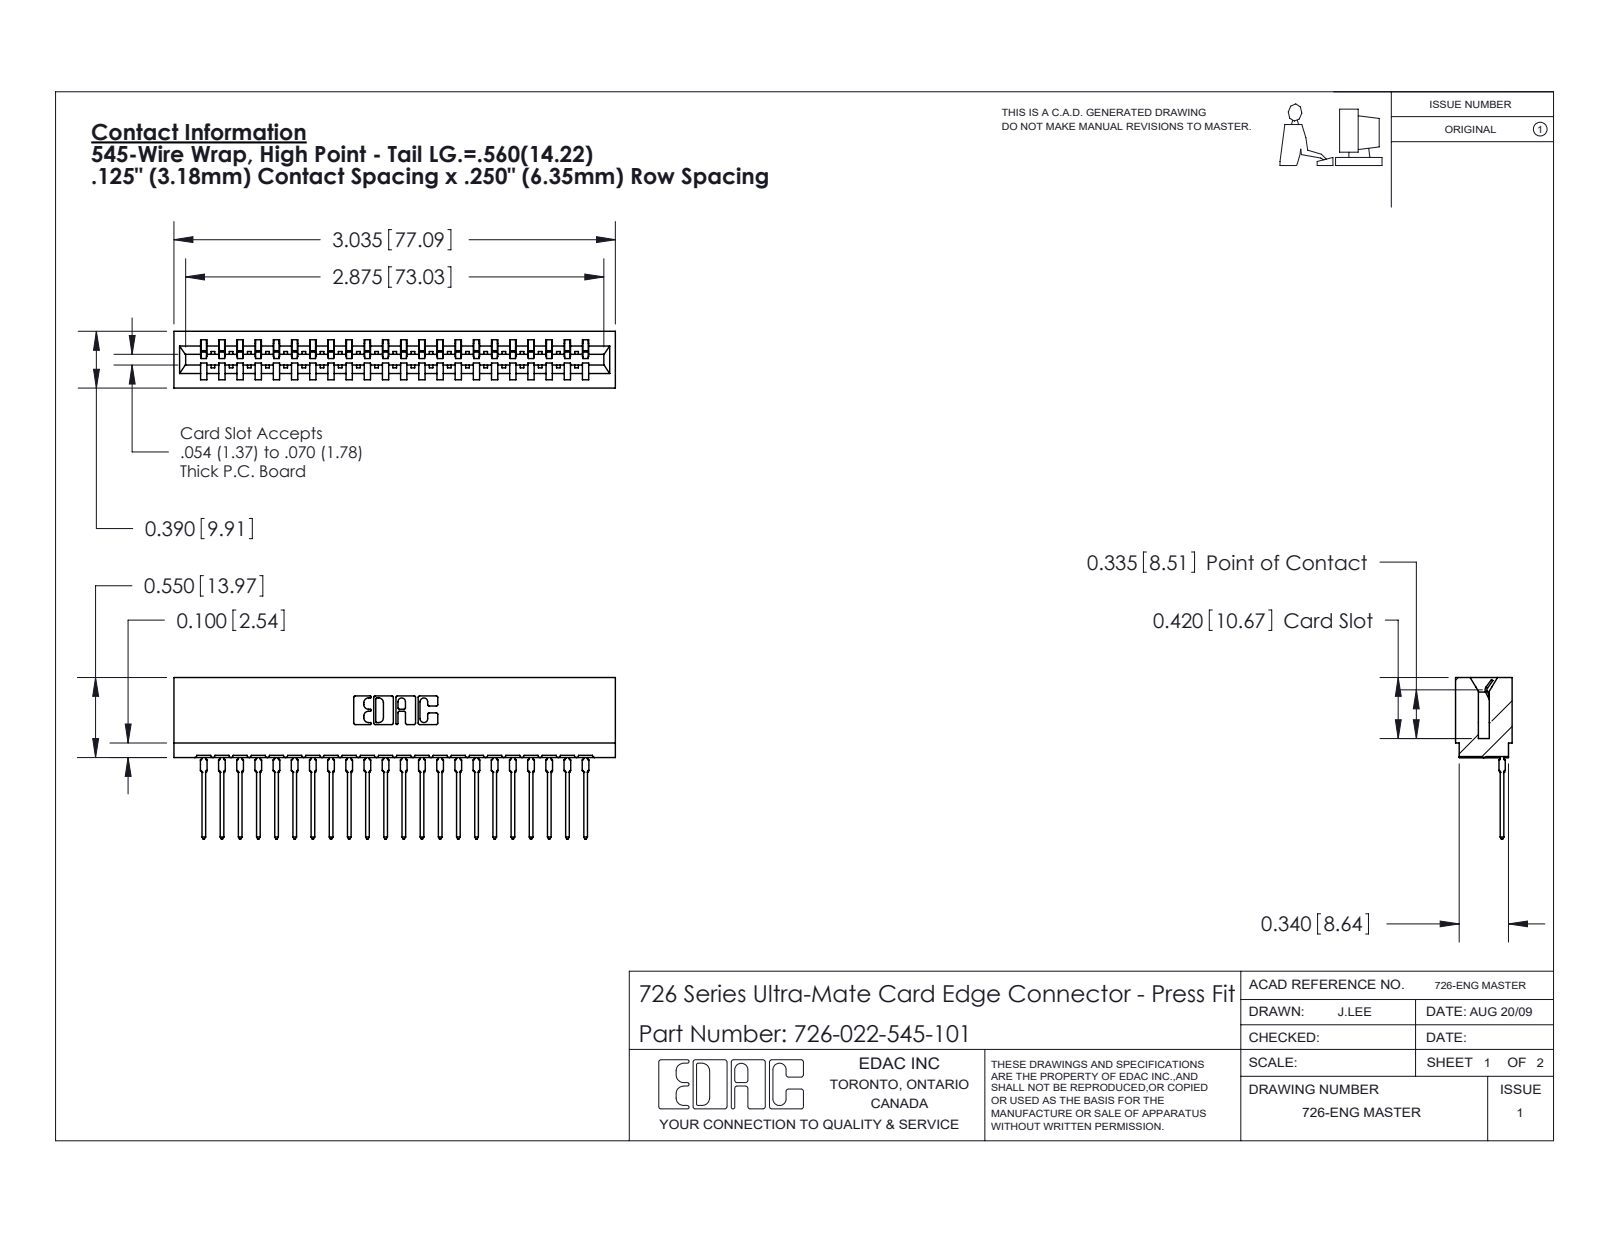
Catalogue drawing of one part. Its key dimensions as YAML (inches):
part_name: "746-292-001_545; 726 Part_.515 Slot Depth - 01; 726-022-545-101"
step_written_by: "SolidWorks 2020 (CONFIG_CONTROL_DESIGN)"
units: inches
bodies: {solids: 23, faces: 2473, planar: 1441, cylindrical: 460, other: 572}
overall_size: [3.035, 1.109, 0.39]
volume: 0.431
surface_area: 16.72
partial_cylinders:
  - {radius: 0.021, count: 44}
  - {radius: 0.015, count: 23}
  - {radius: 0.01, count: 22}
  - {radius: 0.007, count: 6}
  - {radius: 0.031, count: 6}
  - {radius: 0.005, count: 4}
  - {radius: 0.011, count: 4}
  - {radius: 0.026, count: 3}
face_to_face_distances: [0.057, 0.333, 0.39, 0.025, 0.307, 0.25, 0.083, 0.042, 1.25, 0.125]
